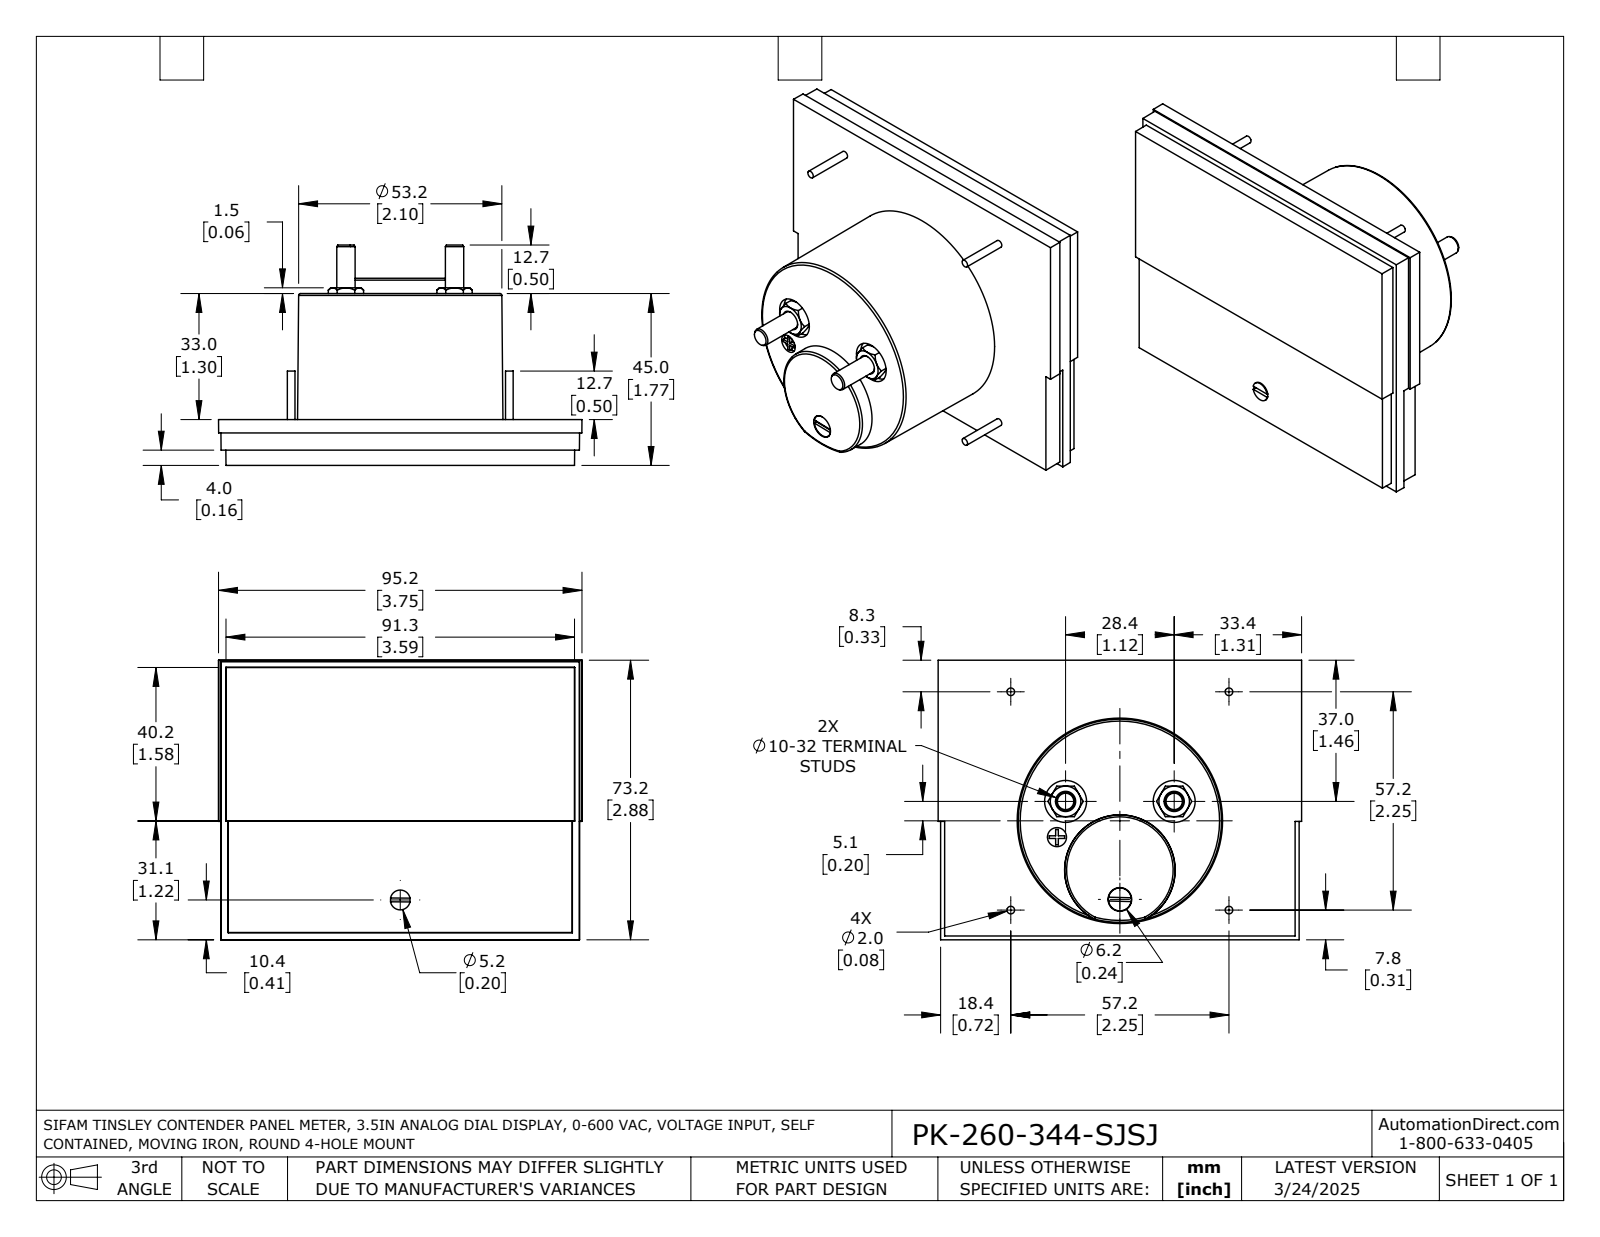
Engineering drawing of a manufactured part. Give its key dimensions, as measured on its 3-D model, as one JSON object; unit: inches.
{"part_name": "PK-260-344-SJSJ", "step_written_by": "SolidWorks 2021 (AUTOMOTIVE_DESIGN)", "units": "inches", "bodies": {"solids": 1, "faces": 163, "planar": 76, "cylindrical": 31, "other": 56}, "overall_size": [3.748, 2.882, 2.272], "volume_in3": 9.446, "surface_area_in2": 38.39, "round_holes": [[0.433, 2], [0.197, 1], [0.244, 1]], "round_bosses_or_shafts": [[0.079, 4], [0.189, 2], [0.236, 1], [0.205, 1]], "partial_cylinders_radius": [[0.1, 1]], "face_to_face_distances": [0.472, 0.03, 0.443, 1.772, 1.299, 1.742, 0.157, 0.073, 0.315, 1.457], "hole_center_spacings": [1.155, 0.379, 0.912, 1.12, 1.263]}
